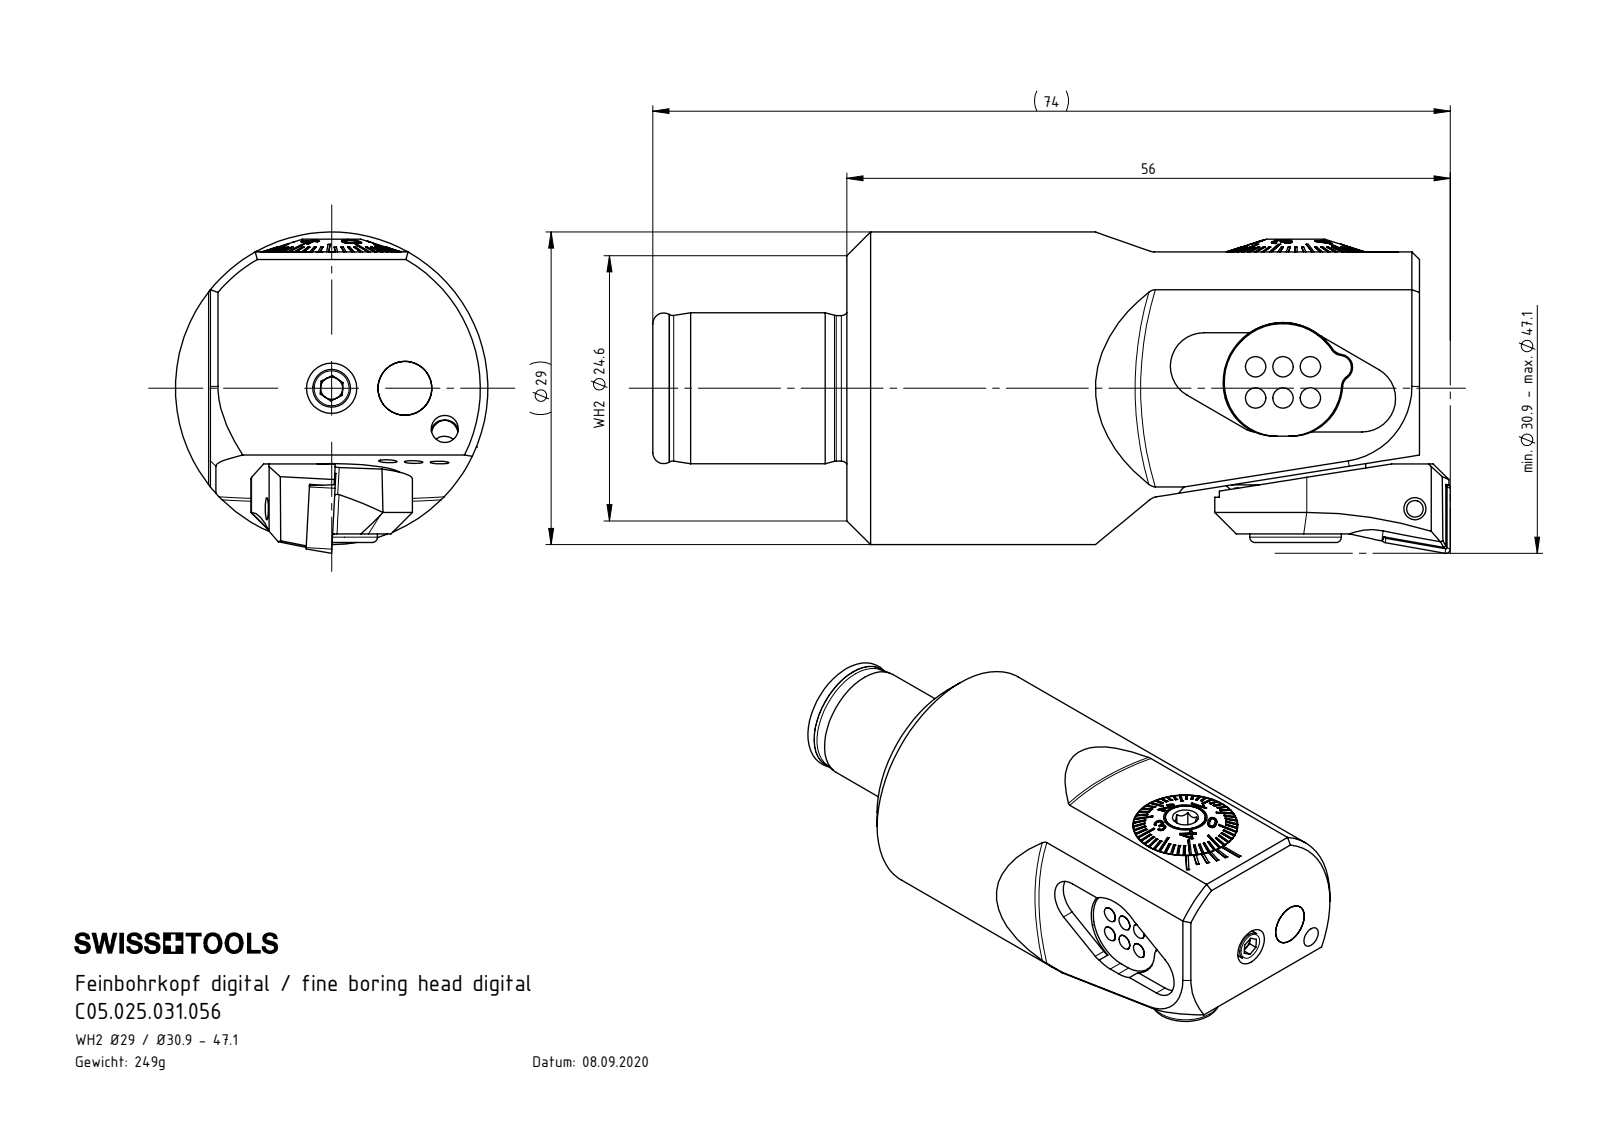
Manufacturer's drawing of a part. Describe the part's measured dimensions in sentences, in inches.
The part is named "F25-BG2.010.011_A; Klebstoff D5; DIN 7984 - M5 x 8; WH2-F25.DA3.056_A_Aktuell 06.2014-180ø-M1x2 Abstand+0.7 versetzt 0.62 (+8 more)". Its 3-D file was written by "SolidWorks 2017 (CONFIG_CONTROL_DESIGN)". It is 15 solids with 804 faces: 405 planar, 142 cylindrical and 257 other. Overall it measures 2.801 by 1.142 by 1.142 inches. Its volume is 1.92 cubic inches and its surface area 20.21 square inches. Round holes: 3 of diameter 0.059, 2 of diameter 0.098, 2 of diameter 0.165, 2 of diameter 0.197, 1 of diameter 0.081, 1 of diameter 0.094, 1 of diameter 0.106, 1 of diameter 0.118, 1 of diameter 0.13, 1 of diameter 0.217, 1 of diameter 0.252, 1 of diameter 0.287. Round bosses or shafts: 6 of diameter 0.075, 2 of diameter 0.197, 2 of diameter 0.195, 1 of diameter 1.142, 1 of diameter 0.551, 1 of diameter 0.531, 1 of diameter 0.512, 1 of diameter 0.511. Partial cylindrical surfaces (rounded edges, fillets, slot ends): 4 of radius 0.055, 3 of radius 0.043, 3 of radius 0.047, 2 of radius 0.02, 2 of radius 0.059, 2 of radius 0.122, 2 of radius 0.189, 2 of radius 0.193. The main face-to-face distances are 2.093, 0.059, 0.709, 0.063, 0.154, 0.122, 0.032, 0.175, 0.091, 2.801. The hole center spacings are 0.056, 0.268, 0.288, 0.344.
